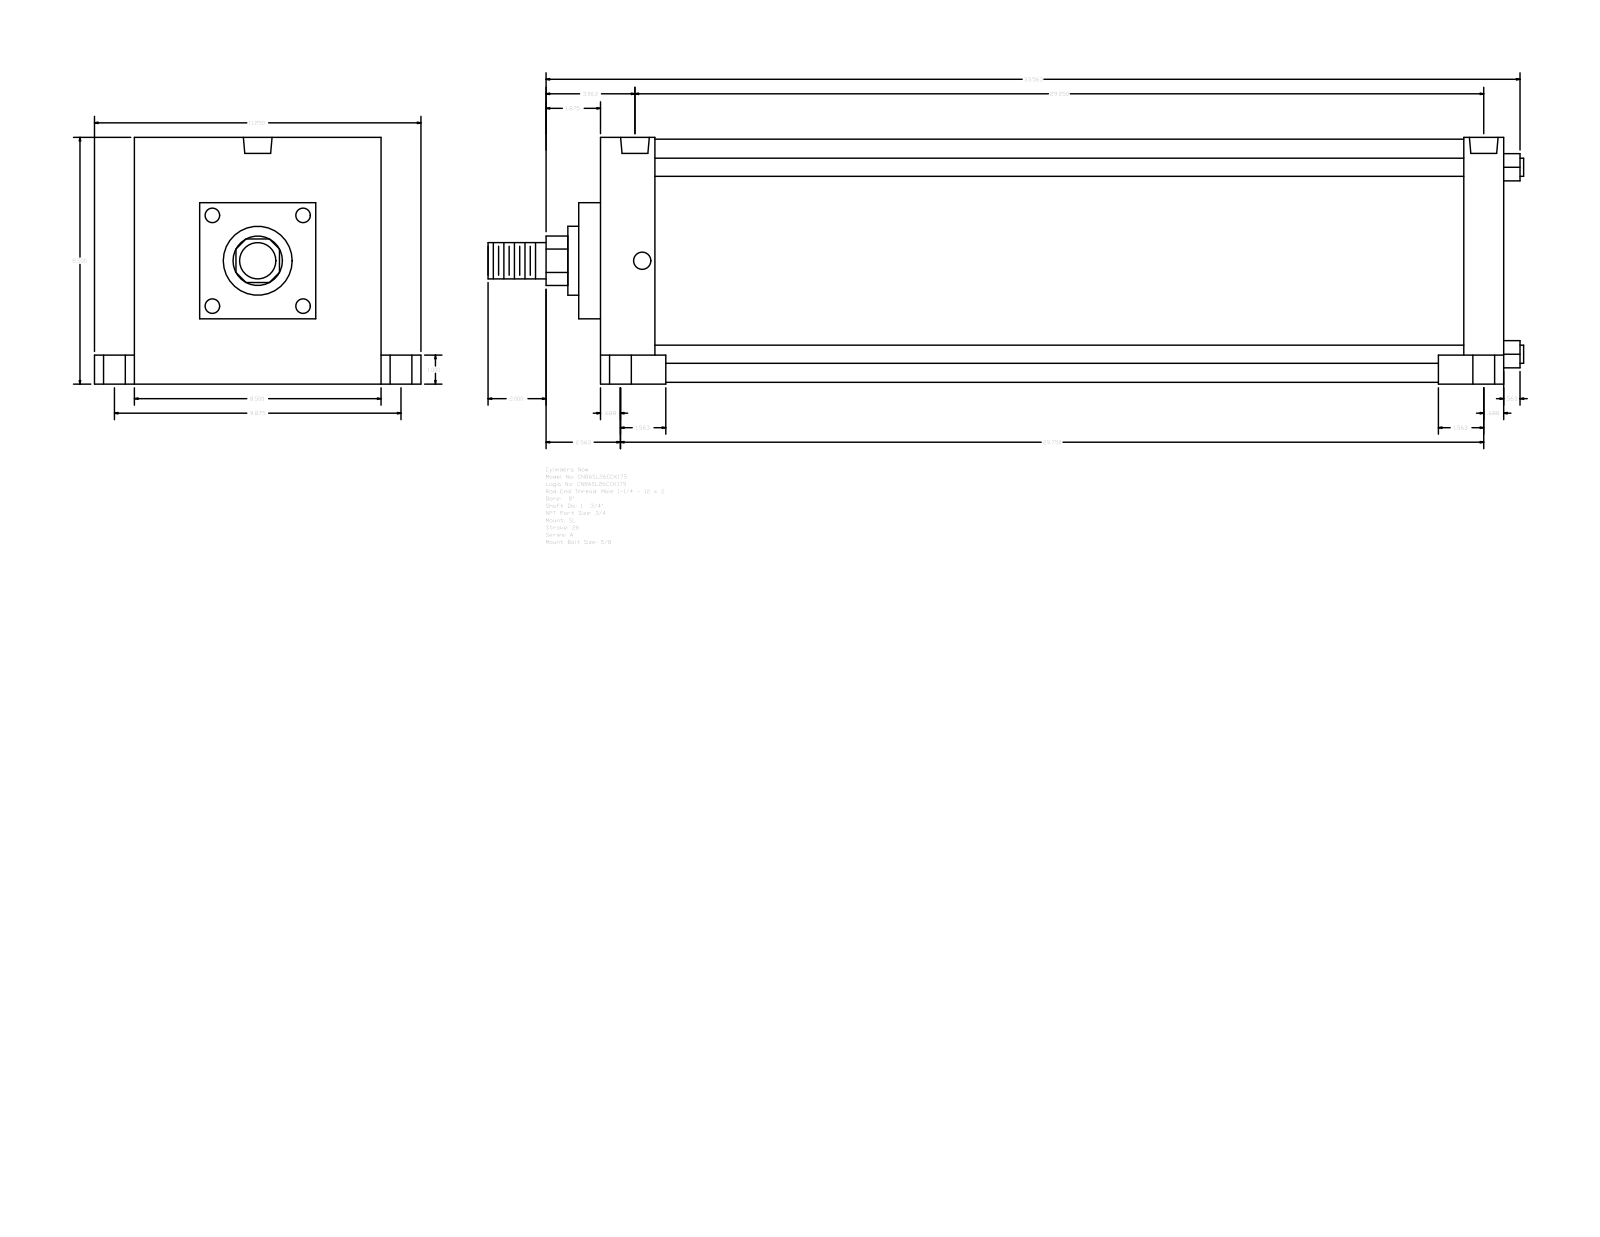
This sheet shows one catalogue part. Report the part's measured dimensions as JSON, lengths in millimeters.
{"part_name": "A_SL__0800_1.75", "step_written_by": "GSSL Pune (CONFIG_CONTROL_DESIGN)", "units": "millimeters", "bodies": {"solids": 0, "faces": 117, "planar": 85, "cylindrical": 32, "other": 0}, "overall_size": [906.46, 285.75, 215.9], "round_holes": [[15.08, 4], [19.05, 4], [25.4, 4], [25.12, 2]], "round_bosses_or_shafts": [[15.88, 4], [212.72, 1], [60.33, 1], [44.45, 1], [31.75, 1]], "partial_cylinders_radius": [[21.63, 1]], "face_to_face_distances": [790.58, 215.9, 34.93, 47.63, 742.95, 755.65, 708.02, 57.15, 19.05, 158.75], "hole_center_spacings": [6.35, 125.41, 125.57, 126.05, 126.85, 250.82, 730.25, 736.6]}
